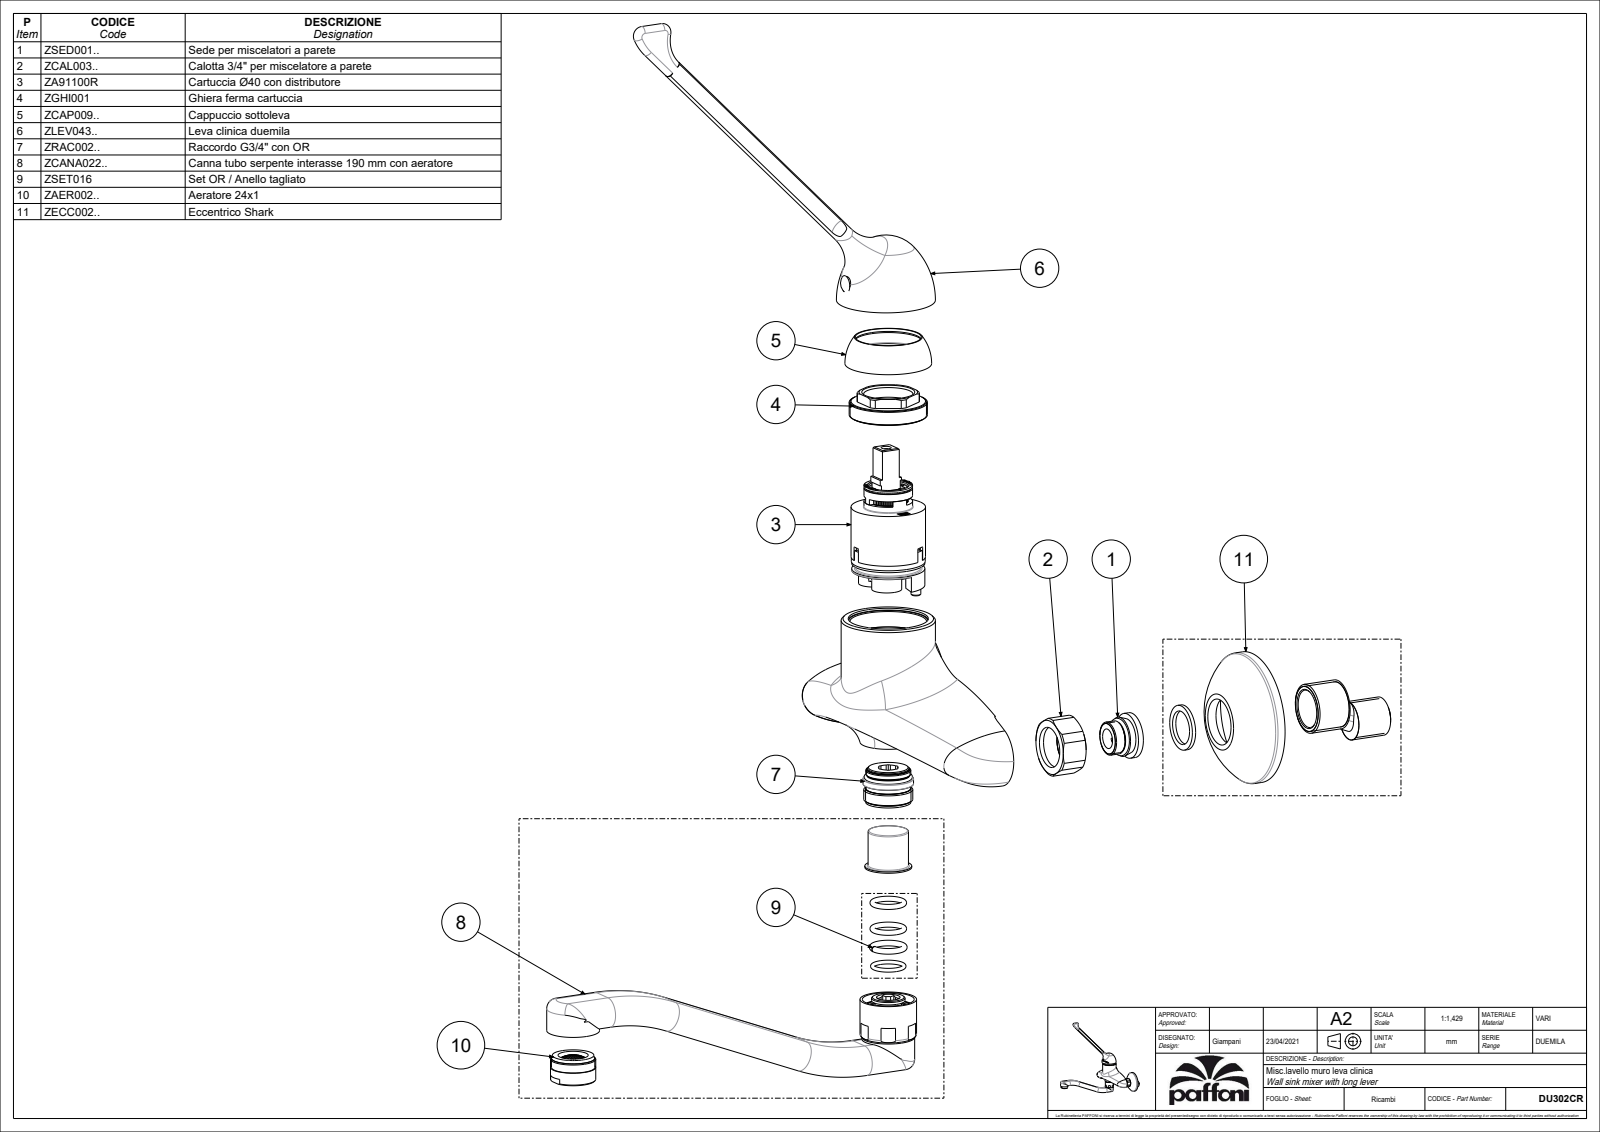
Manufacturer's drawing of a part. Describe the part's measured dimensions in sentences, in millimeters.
The part is named "DU302CR". Its 3-D file was written by "CREO PARAMETRIC BY PTC INC, 2020044 (CONFIG_CONTROL_DESIGN)". It is 2 solids with 346 faces: 106 planar, 101 cylindrical and 139 other. Overall it measures 281.7 by 266.5 by 220 millimeters. Its volume is 484 088 cubic millimeters and its surface area 113 180 square millimeters. Round holes: 2 of diameter 16, 1 of diameter 5, 1 of diameter 6, 1 of diameter 17.2, 1 of diameter 18.2, 1 of diameter 18.5, 1 of diameter 20, 1 of diameter 21, 1 of diameter 21.2, 1 of diameter 23.3, 1 of diameter 27, 1 of diameter 35. Round bosses or shafts: 2 of diameter 70, 2 of diameter 28, 2 of diameter 24, 1 of diameter 50, 1 of diameter 30, 1 of diameter 26.8, 1 of diameter 26, 1 of diameter 10. Partial cylindrical surfaces (rounded edges, fillets, slot ends): 6 of radius 7.2, 6 of radius 8, 2 of radius 3, 2 of radius 15.5, 2 of radius 20.5, 2 of radius 94, 2 of radius 94.8, 2 of radius 109.2. The main face-to-face distances are 34.5, 0.8, 15.2, 35.5, 6, 1, 1.5, 14.4, 16, 0.5. The hole center spacings are 193.
